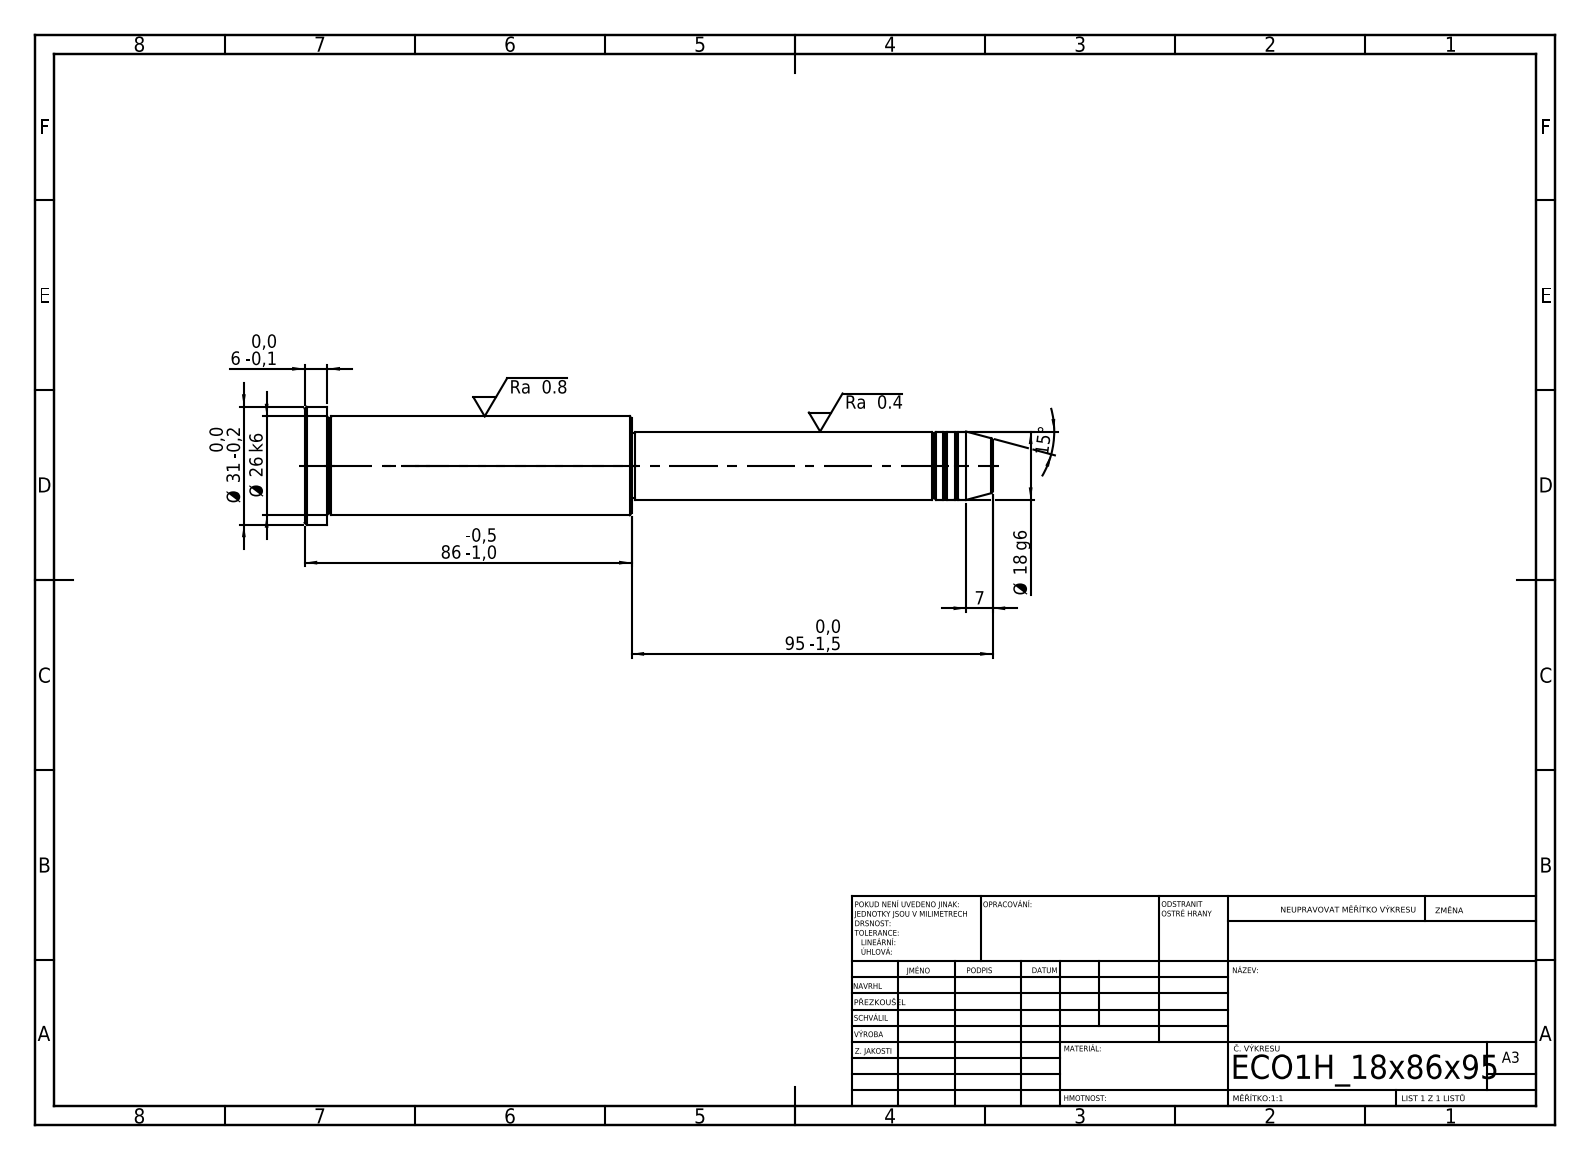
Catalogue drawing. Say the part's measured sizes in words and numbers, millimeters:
Its 3-D file was written by "SolidWorks 2019 (CONFIG_CONTROL_DESIGN)". It is 1 solid with 43 faces: 5 planar, 14 cylindrical and 24 other. Overall it measures 181 by 31 by 31 millimeters. Its volume is 70 685 cubic millimeters and its surface area 14 001 square millimeters. Round bosses or shafts: 1 of diameter 31, 1 of diameter 26, 1 of diameter 18, 1 of diameter 17. The main face-to-face distances are 86, 80, 6, 95, 175, 181, 94, 1, 81, 87.
